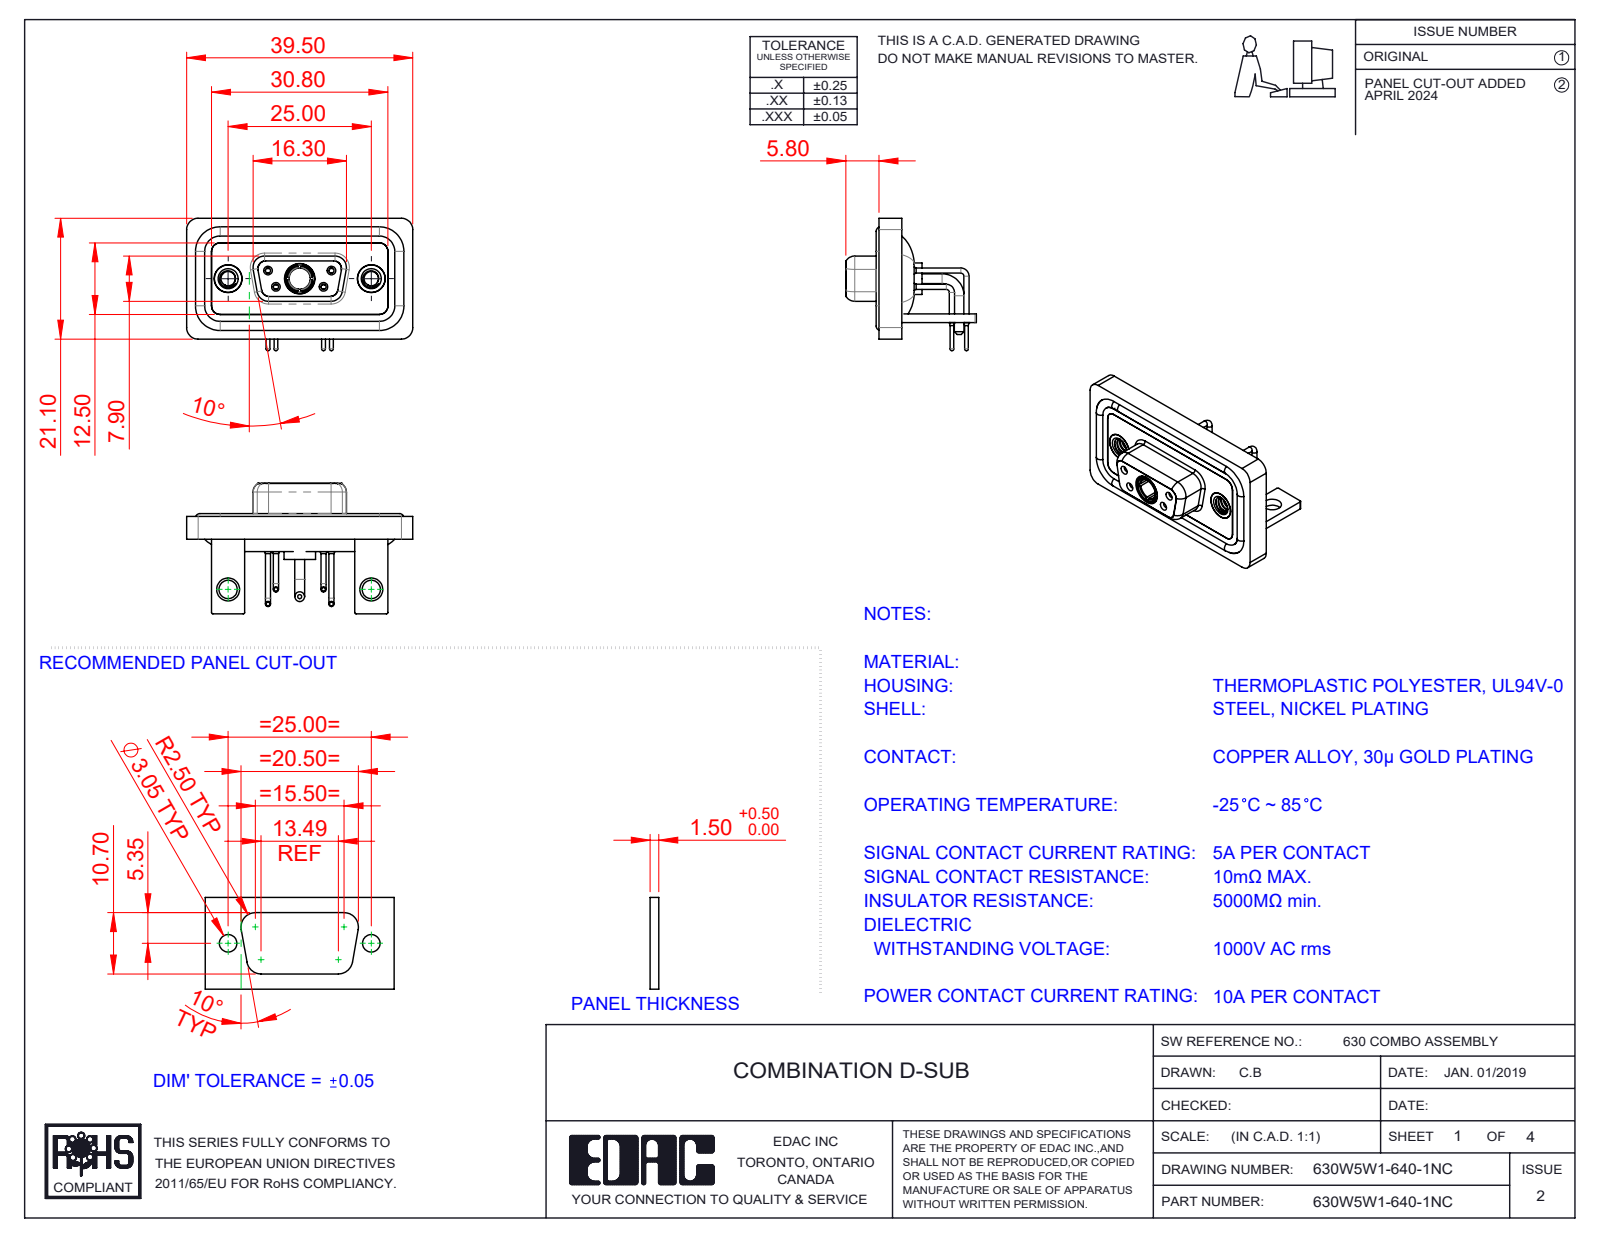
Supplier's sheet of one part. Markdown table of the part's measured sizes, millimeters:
| quantity | value |
| --- | --- |
| part name | 630Combo Stabilizer Bracket_50 Contacts; 630Combo Waterproof Housing_09 Contacts; 630Combo Contact Row 2_50 Contacts; Power Socket_10A RA (+6 more) |
| STEP written by | SolidWorks 2023 (CONFIG_CONTROL_DESIGN) |
| units | millimeters |
| bodies | 15 solids, 718 faces (214 planar, 327 cylindrical, 177 other) |
| overall size | 39.5 × 23.12 × 22.8 |
| volume | 5 130 mm³ |
| surface area | 8 531 mm² |
| round holes (diameter × count) | 0.9 × 4, 1.1 × 4, 1.5 × 4, 2 × 4, 4.85 × 3, 1.6 × 2, 1.7 × 2, 2.5 × 2, 3.2 × 2, 4 × 2, 4.05 × 2, 5 × 2 |
| round bosses / shafts (diameter × count) | 1.6 × 6, 0.9 × 4, 0.65 × 4, 4.95 × 2, 4.8 × 2, 1.7 × 2, 5.5 × 1, 5.2 × 1 |
| partial cylindrical surfaces (radius × count) | 2 × 19, 1.5 × 18, 0.25 × 16, 1.35 × 8, 1.6 × 8, 0.5 × 5, 0.6 × 4, 0.65 × 4 |
| main face-to-face distances | 0.4, 2.9, 1.5, 1.8, 1.1, 3.7, 1.6, 0.8, 2.5, 3.1 |
| hole center spacings | 3.16, 5.72, 7.1, 12.5, 18.1, 25, 4.39, 4.4 |
